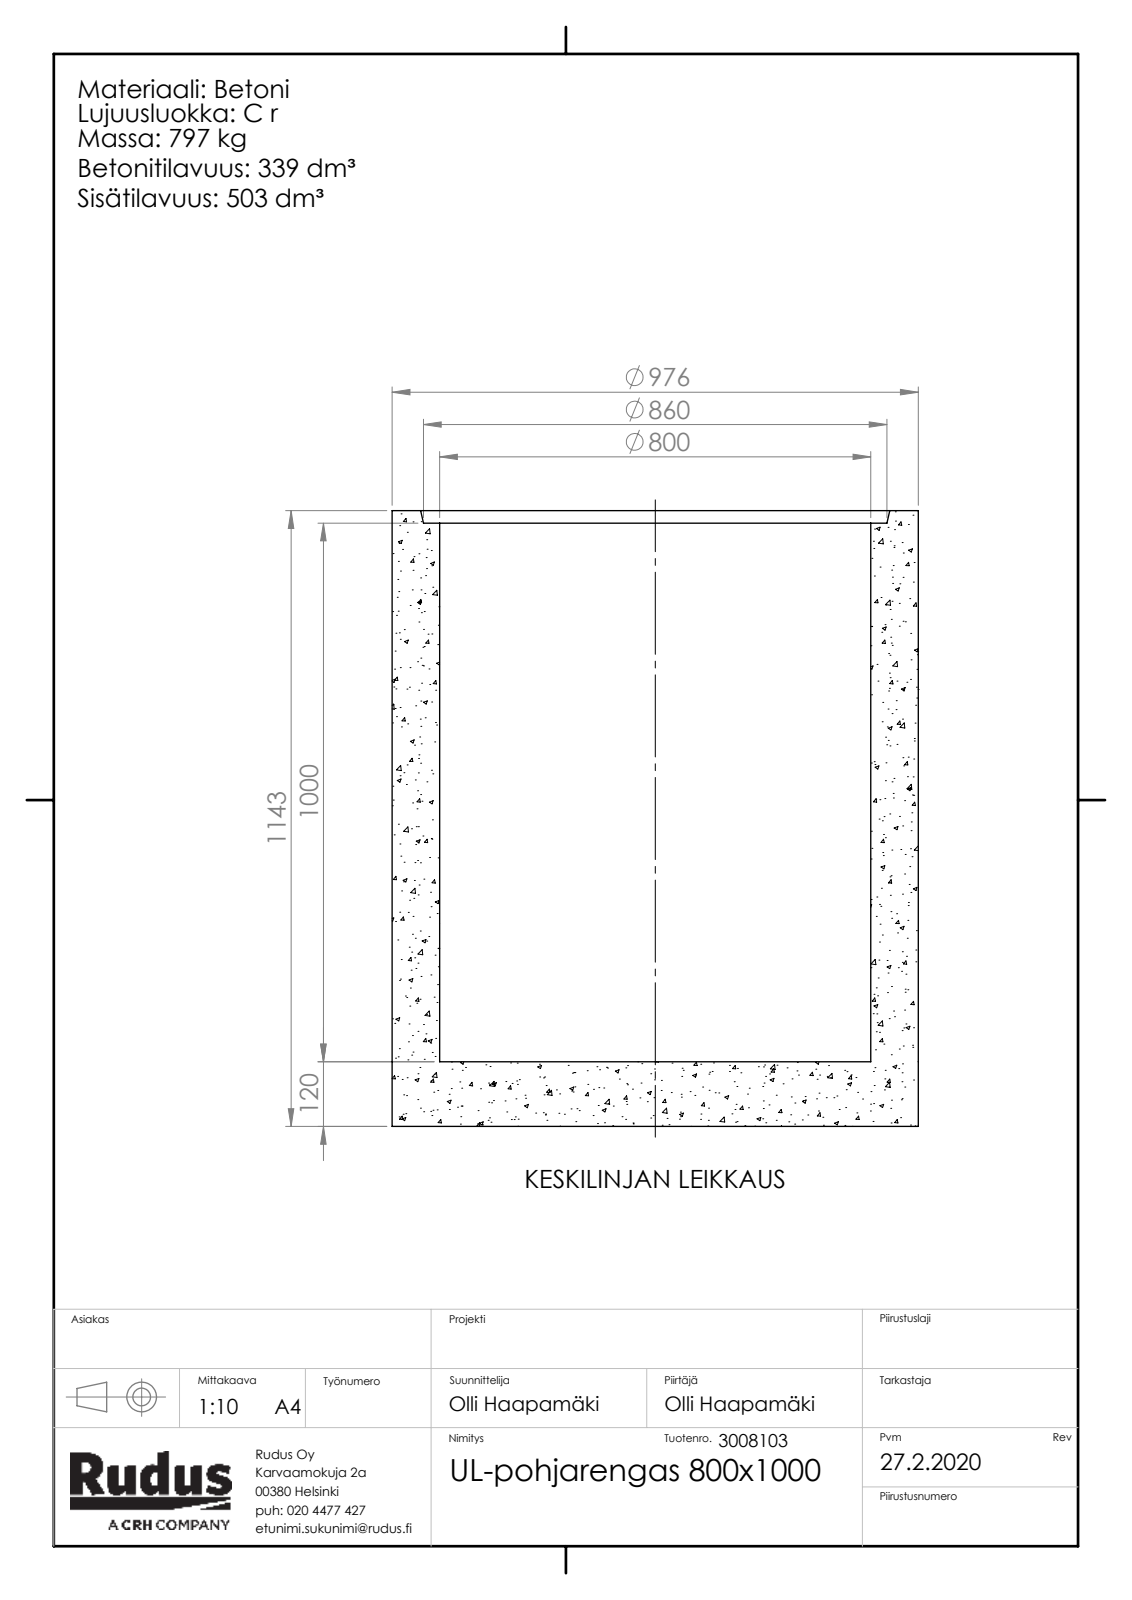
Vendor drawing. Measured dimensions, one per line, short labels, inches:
name: EK-osa-kaivorunko_UL-pohjarengas; Rudus 3008103 UL-pohjarengas 800x1000
written by: SolidWorks 2019 (CONFIG_CONTROL_DESIGN)
unit: in
bodies: 1 solid, 89 faces (4 planar, 2 cylindrical, 83 other)
size: 45 × 38.425 × 38.425
volume: 20 690 in³; area: 11 730 in²
bosses: 1× ⌀38.425
face distances: 4.724, 45, 40.276, 44.094, 39.37, 0.906
